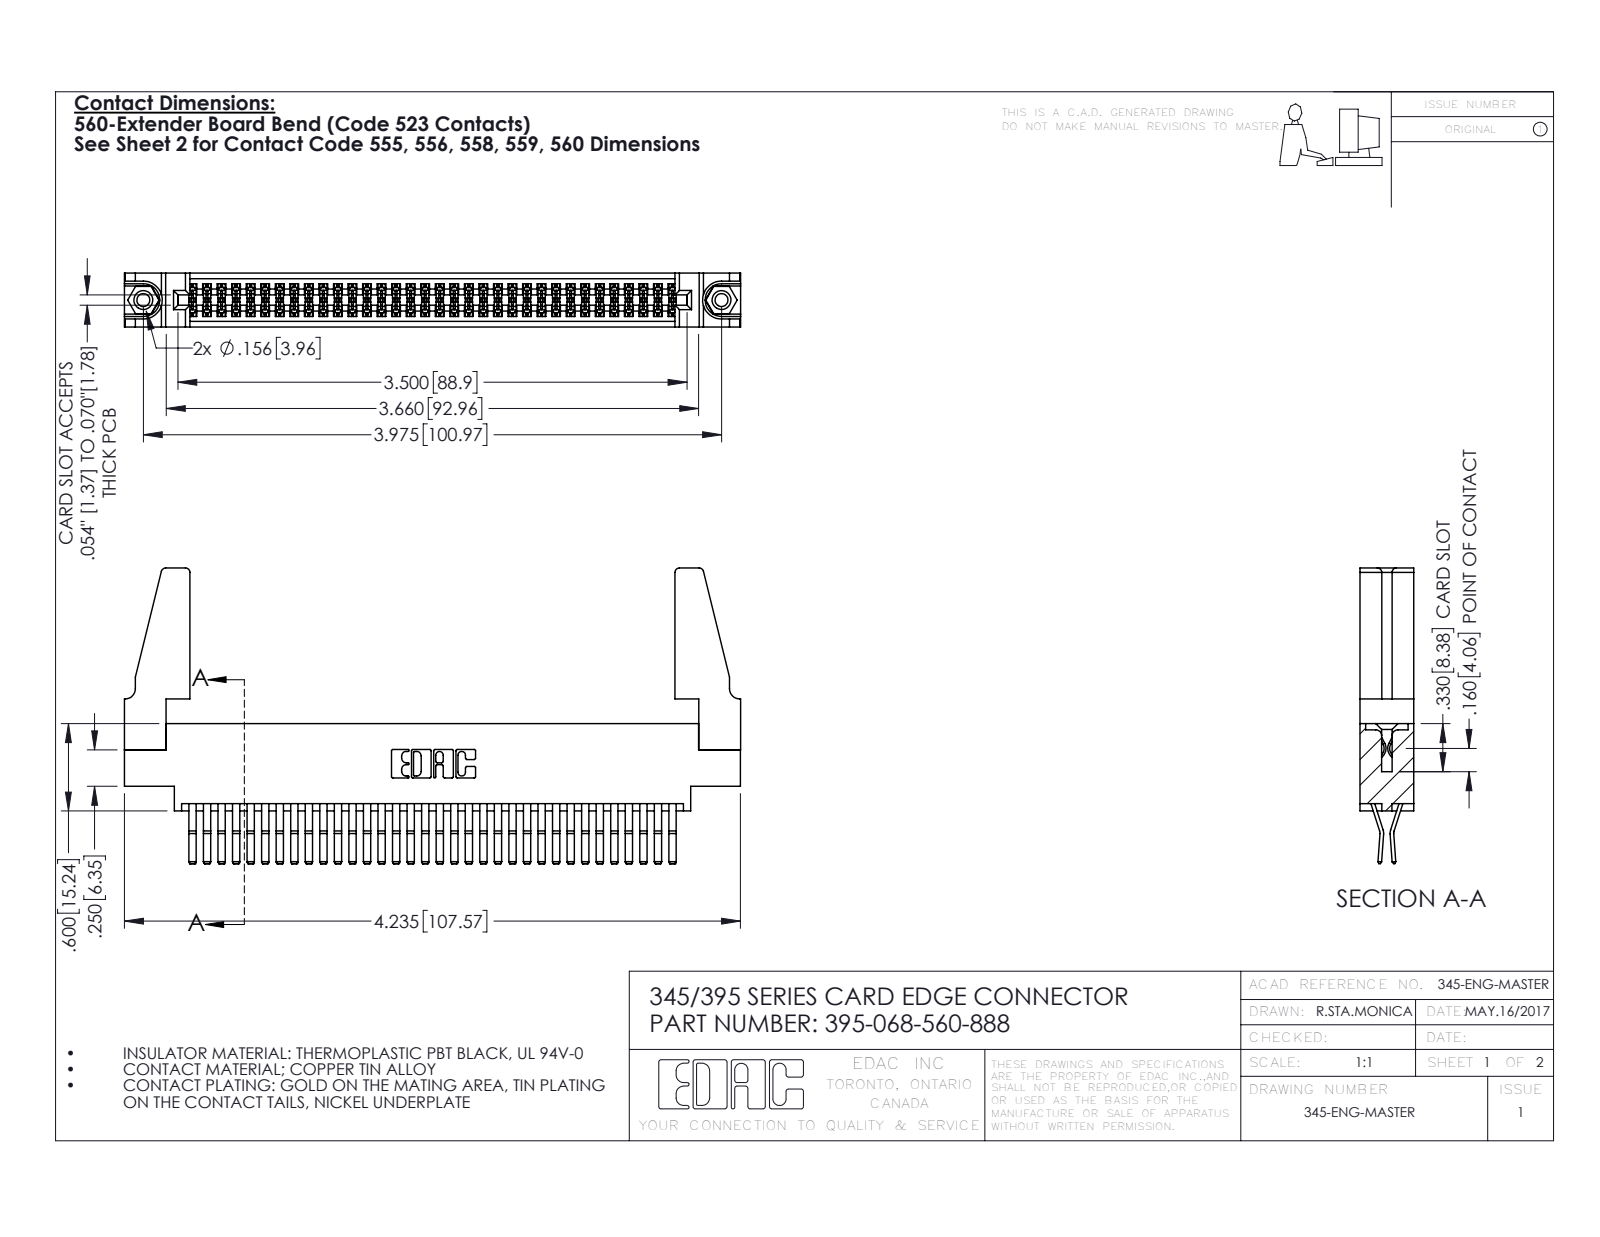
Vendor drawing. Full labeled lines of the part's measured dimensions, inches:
Part name (STEP PRODUCT): 345-250-001_345-250-001-102; 345 Part_0.170 Offset - 0.156 Dia-TH; 395-068-560-888; 345-220-078_345-220-088 (+1 more)
STEP written by: SolidWorks 2016 (CONFIG_CONTROL_DESIGN)
Units: inches
Bodies: 73 solids, 3790 faces (2400 planar, 1374 cylindrical, 16 other)
Overall size (bounding box): 4.236 × 2.032 × 0.37
Volume: 0.852 in³ · Surface area: 31.14 in²
Round holes (diameter × count): ⌀0.089 ×2, ⌀0.125 ×2, ⌀0.156 ×2, ⌀0.064 ×1
Round bosses / shafts (diameter × count): ⌀0.155 ×2
Partial cylindrical surfaces — rounded edges, fillets, slot ends (radius × count): R0.006 ×102, R0.01 ×22, R0.03 ×8, R0.007 ×6, R0.031 ×6, R0.026 ×3, R0.01 ×2, R0.014 ×2
Main face-to-face distances: 0.072, 0.37, 0.298, 0.025, 0.2, 0.098, 0.272, 0.225, 0.175, 0.149
Hole centre spacings: 0.27, 3.74, 3.975
